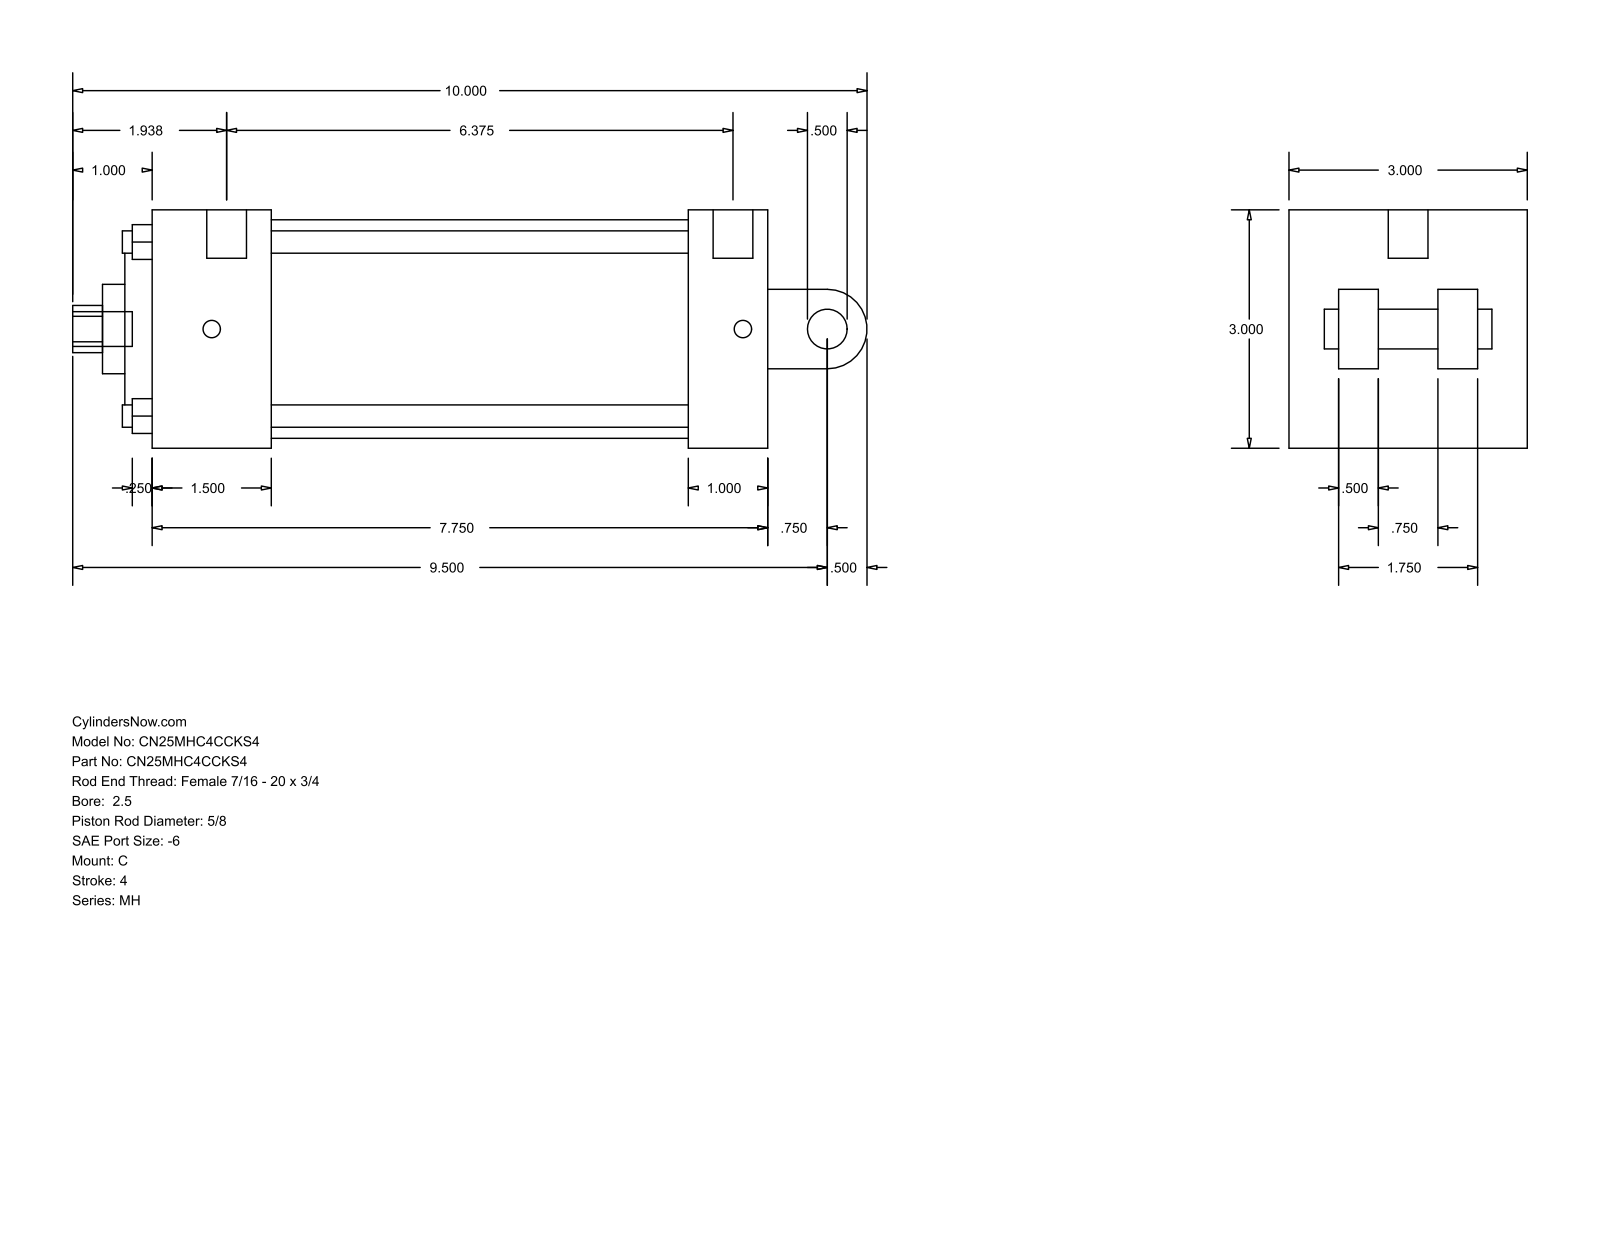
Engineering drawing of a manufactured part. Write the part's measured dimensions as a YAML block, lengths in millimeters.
part_name: "MH_C__0250_0.625"
step_written_by: "GSSL Pune (CONFIG_CONTROL_DESIGN)"
units: millimeters
bodies: {solids: 0, faces: 101, planar: 71, cylindrical: 30, other: 0}
overall_size: [254, 76.2, 76.2]
round_holes:
  - {diameter: 7.14, count: 4}
  - {diameter: 5.56, count: 2}
  - {diameter: 12.7, count: 1}
  - {diameter: 15.88, count: 1}
  - {diameter: 28.57, count: 1}
  - {diameter: 55.55, count: 1}
  - {diameter: 69.85, count: 1}
round_bosses_or_shafts:
  - {diameter: 12.7, count: 2}
  - {diameter: 5.56, count: 2}
  - {diameter: 11.11, count: 1}
partial_cylinders:
  - {radius: 7.54, count: 1}
  - {radius: 12.7, count: 1}
face_to_face_distances: [76.2, 25.4, 196.85, 15.87, 171.45, 38.1, 133.35, 158.75, 8.73, 46.83]
hole_center_spacings: [39.33, 55.62, 78.66, 3.17]
